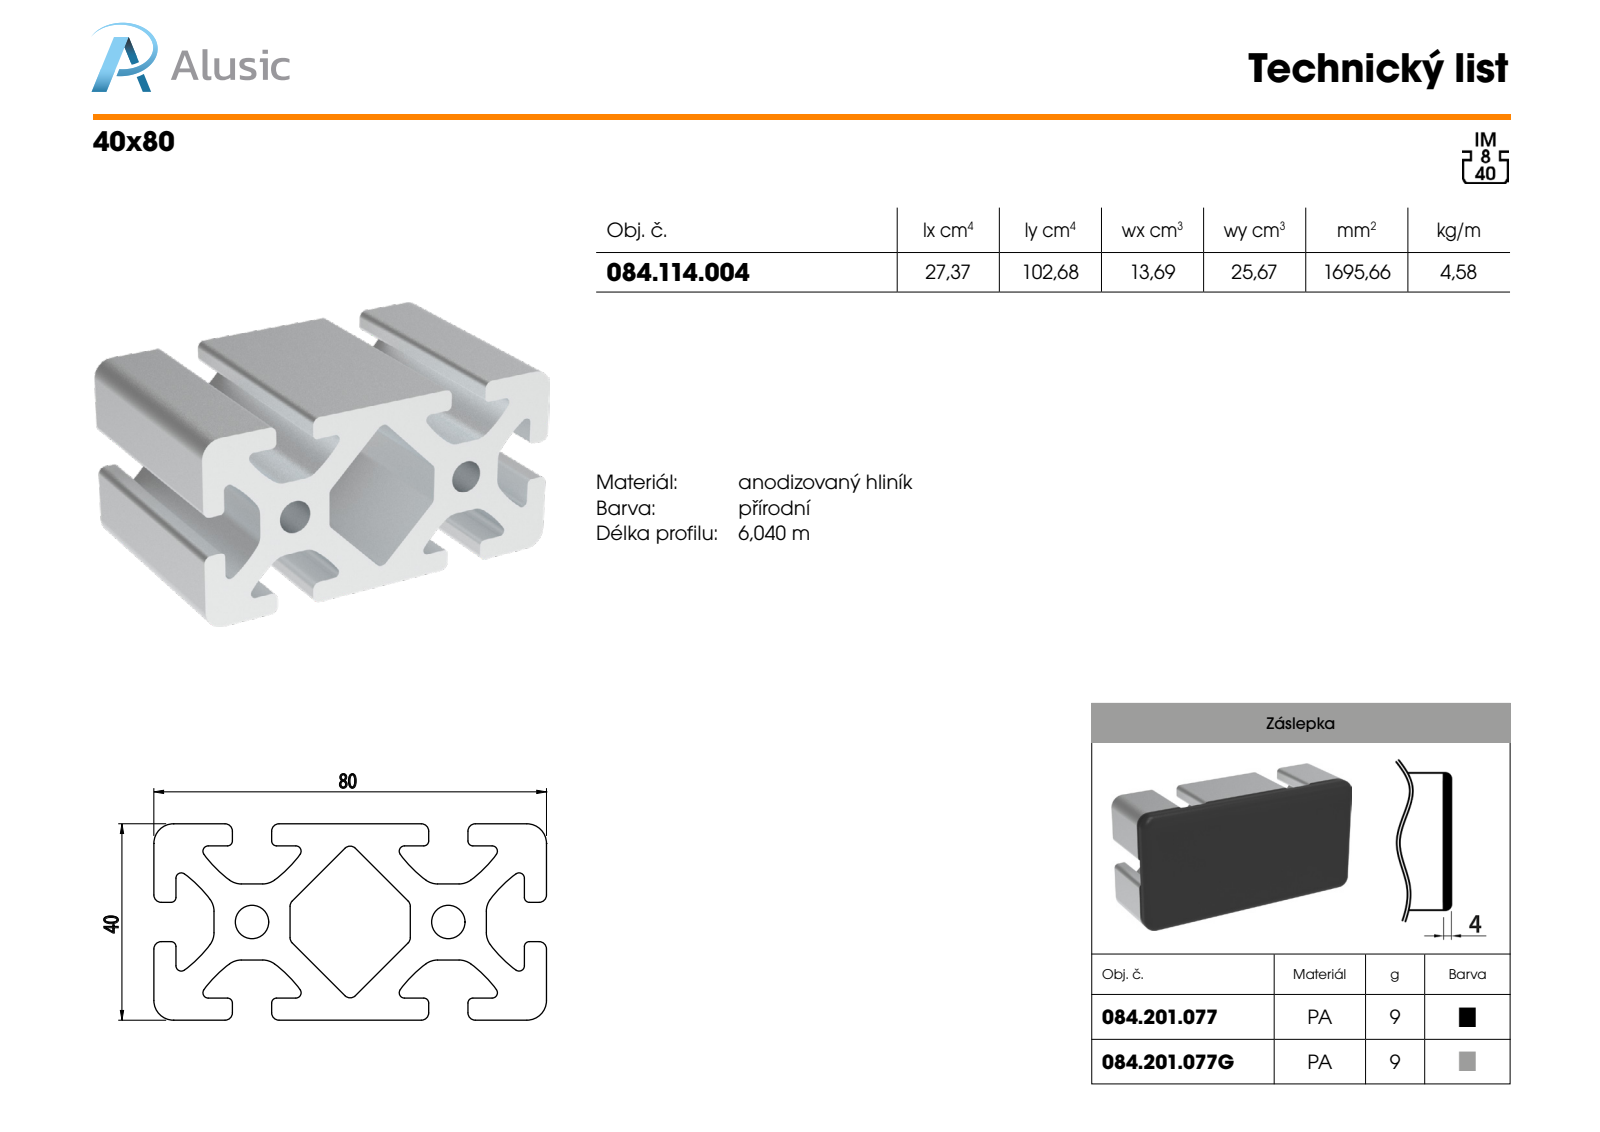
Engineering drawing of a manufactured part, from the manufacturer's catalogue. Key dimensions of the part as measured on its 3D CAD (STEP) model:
Part name (STEP PRODUCT): 084.114.004
STEP written by: SolidWorks 2018 (AUTOMOTIVE_DESIGN)
Units: millimetres
Bodies: 1 solid, 125 faces (48 planar, 77 cylindrical, 0 other)
Overall size (bounding box): 100 × 80 × 40
Volume: 169 242 mm³ · Surface area: 61 794 mm²
Round holes (diameter × count): ⌀6.8 ×2
Partial cylindrical surfaces — rounded edges, fillets, slot ends (radius × count): R1.5 ×20, R4 ×16, R1.08 ×12, R25 ×12, R1 ×10
Main face-to-face distances: 40, 4.5, 22.73, 27.75, 23.25, 35.5, 12.25, 7.75, 3.7, 11.8
Hole centre spacings: 40
